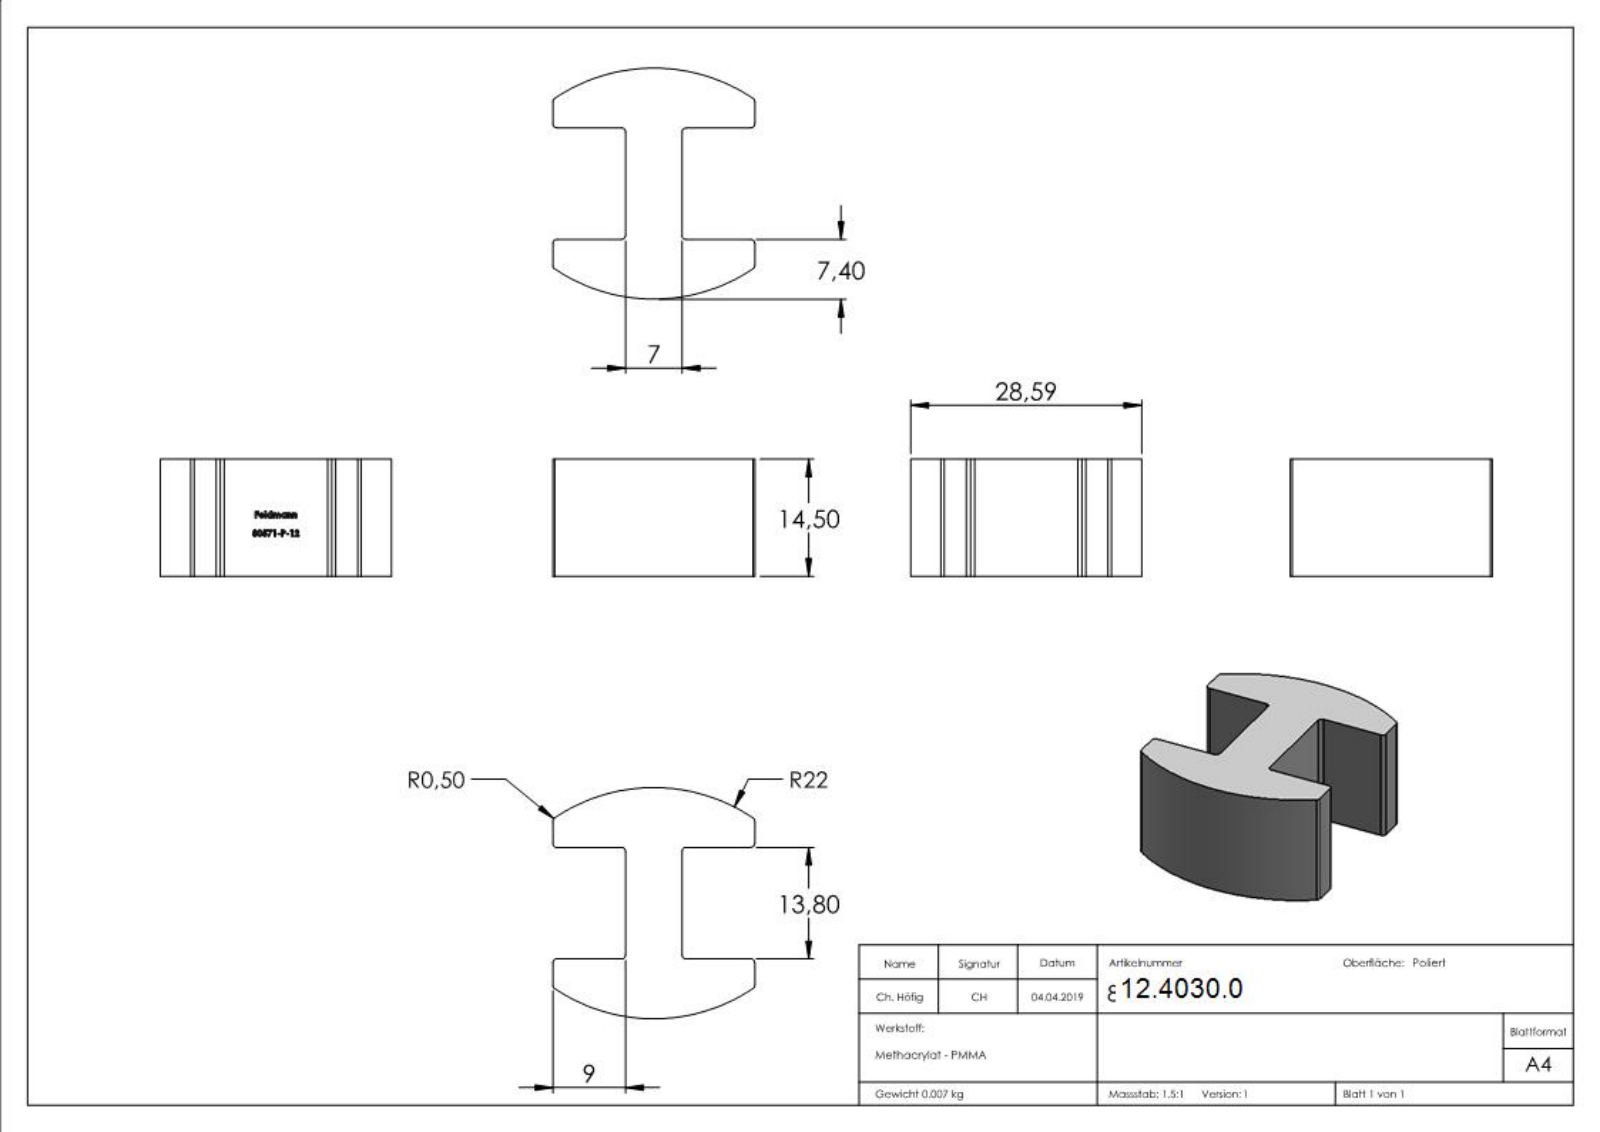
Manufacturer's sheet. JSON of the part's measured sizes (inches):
{"part_name": "80571-P-12", "step_written_by": "SolidWorks 2015 (CONFIG_CONTROL_DESIGN)", "units": "inches", "bodies": {"solids": 1, "faces": 246, "planar": 140, "cylindrical": 15, "other": 91}, "overall_size": [1.126, 0.984, 0.571], "volume_in3": 0.357, "surface_area_in2": 4.157, "partial_cylinders_radius": [[0.02, 12], [0.866, 2]], "face_to_face_distances": [0.571, 0.543, 0.276, 0.354, 0.63, 0.984, 0.626, 0.272, 0.358, 0.285]}
